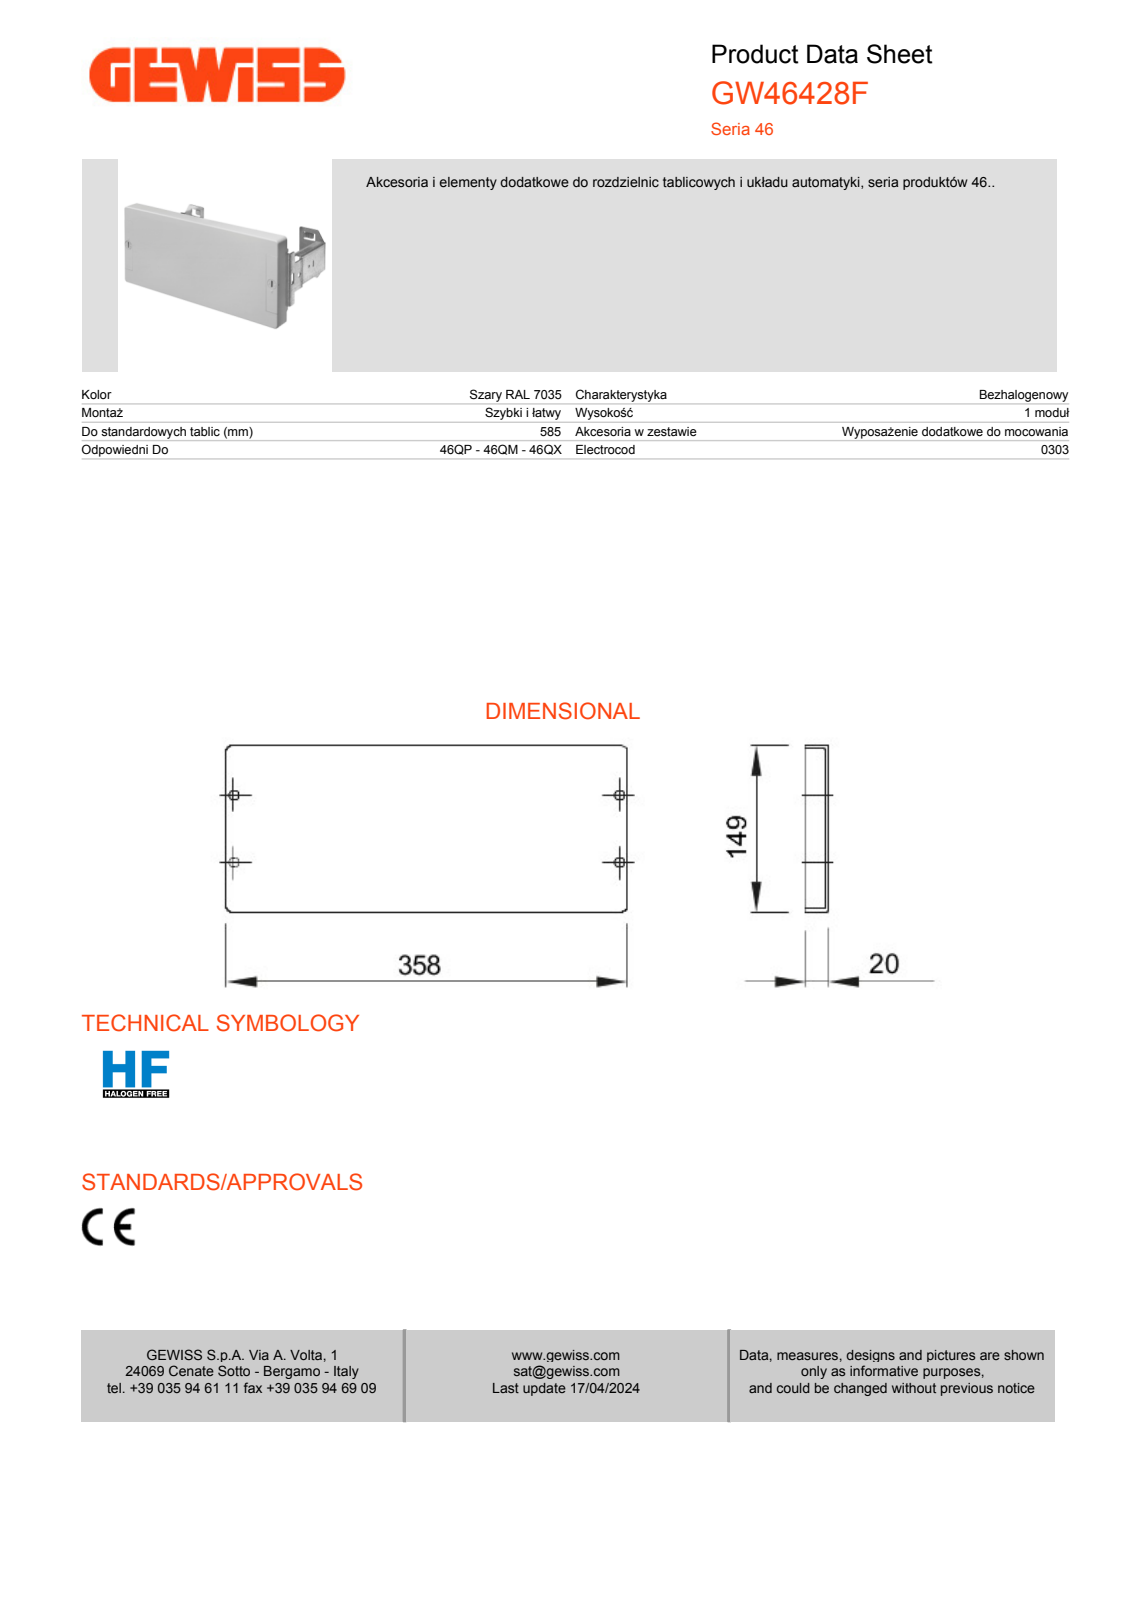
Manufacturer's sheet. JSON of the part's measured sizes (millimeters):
{"part_name": "55711006D2XX_MOSTRINA_CIECA_28M; 55718951FXXX_STAFFA_X_SUPP_GUID; STAFFE_28_ASM; GW46428F_ASM", "step_written_by": "CREO PARAMETRIC BY PTC INC, 2020354 (CONFIG_CONTROL_DESIGN)", "units": "millimeters", "bodies": {"solids": 3, "faces": 564, "planar": 358, "cylindrical": 148, "other": 58}, "overall_size": [543, 149, 119.87], "volume_mm3": 345069, "surface_area_mm2": 253983, "round_holes": [[4.5, 4], [6.5, 4], [5.5, 2], [8, 1]], "round_bosses_or_shafts": [[14.4, 2], [13.4, 2], [9.6, 2]], "partial_cylinders_radius": [[1.5, 28], [1, 20], [1.15, 4], [2, 4], [0.5, 2], [1.25, 2], [2.5, 2], [4, 2]], "face_to_face_distances": [3, 1.5, 17, 93.5, 20, 4, 533.5, 112, 95, 115], "hole_center_spacings": [30.23, 35.11, 507.14, 521.61, 14.5, 60, 502.5, 524.5]}
